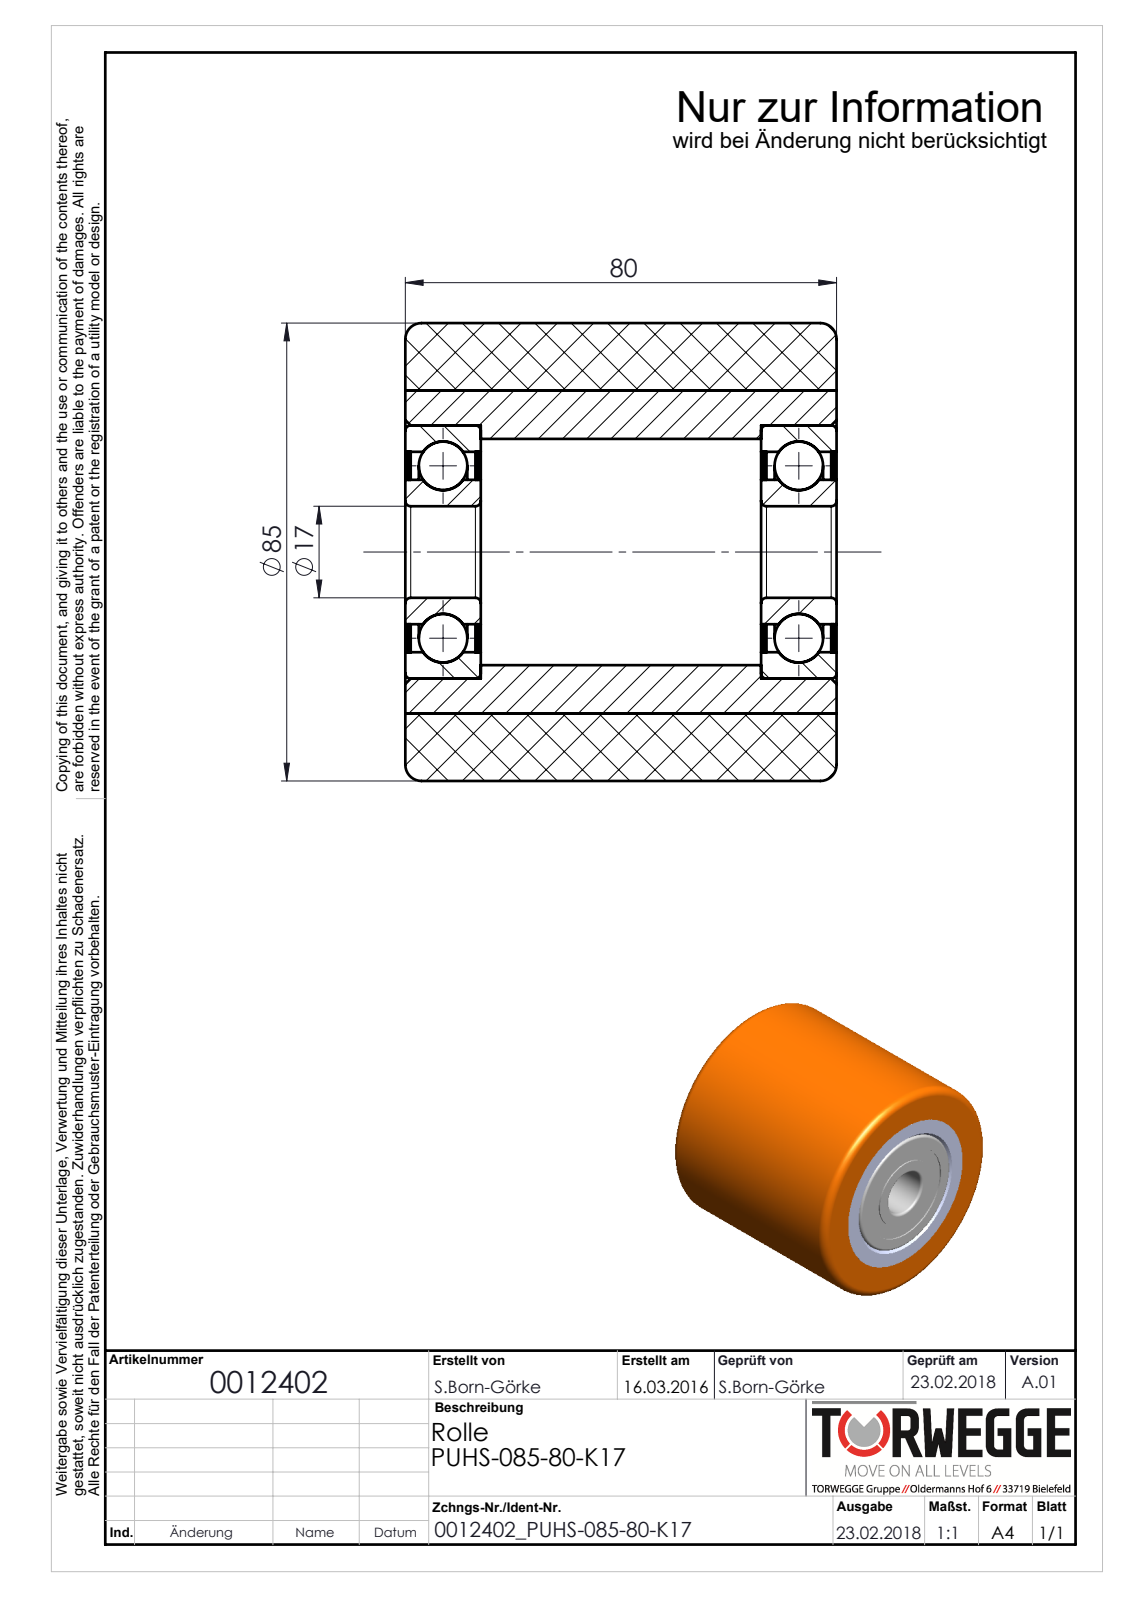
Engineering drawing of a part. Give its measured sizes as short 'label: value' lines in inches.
name: 0012402_PUHS-085-80-K17
written by: SolidWorks 2016 (AUTOMOTIVE_DESIGN)
unit: in
bodies: 12 solids, 118 faces (22 planar, 52 cylindrical, 44 other)
size: 3.346 × 3.346 × 3.15
volume: 22.53 in³; area: 148.6 in²
holes: 1× ⌀0.669, 1× ⌀1.055, 1× ⌀1.465, 1× ⌀1.654, 1× ⌀1.85, 1× ⌀2.362
bosses: 1× ⌀3.346
face distances: 2.598, 0.02, 3.15, 0.512, 0.551, 0.039, 0.531, 2.618, 0.492, 2.579
